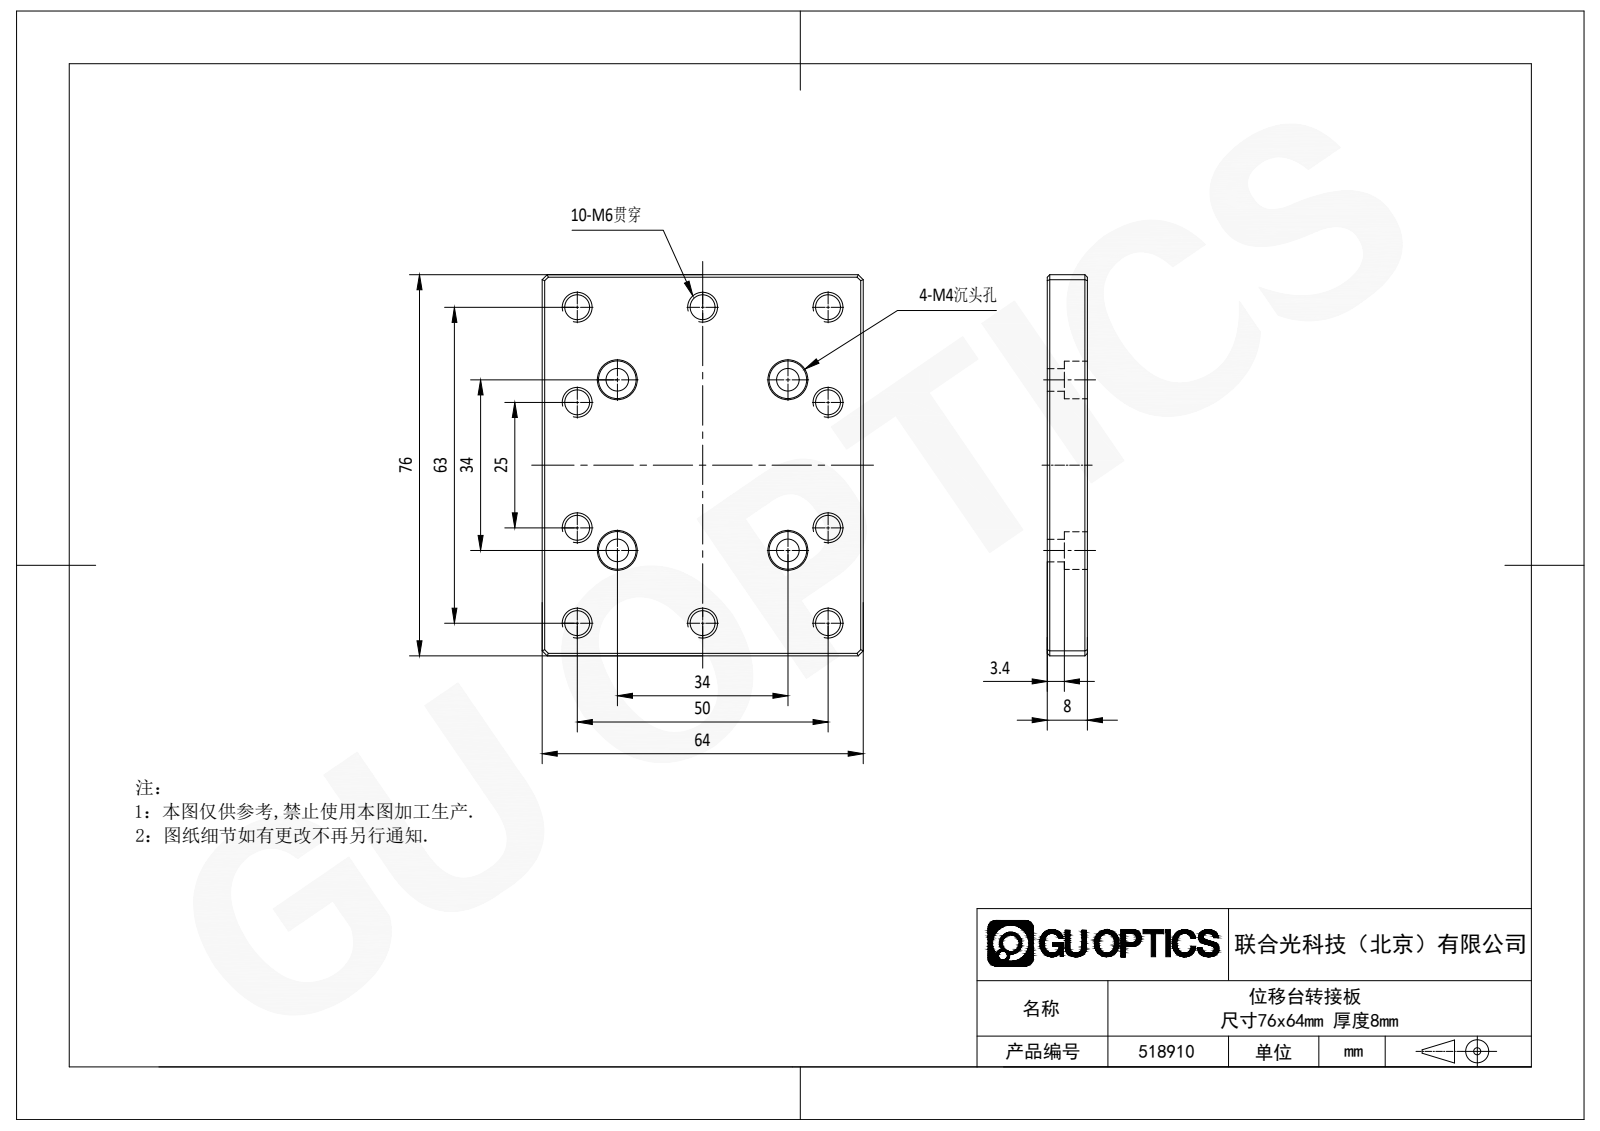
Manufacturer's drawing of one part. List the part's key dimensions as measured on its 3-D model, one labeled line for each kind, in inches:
STEP written by: SolidWorks 2020 (CONFIG_CONTROL_DESIGN)
Units: inches
Bodies: 1 solid, 62 faces (30 planar, 18 cylindrical, 14 other)
Overall size (bounding box): 2.992 × 2.52 × 0.315
Volume: 2.209 in³ · Surface area: 20.28 in²
Round holes (diameter × count): ⌀0.197 ×10, ⌀0.177 ×4, ⌀0.295 ×4
Main face-to-face distances: 0.315, 2.52, 2.992, 0.134, 0.181, 1.976, 2.31, 3.841, 2.911
Hole centre spacings: 0.984, 0.361, 0.652, 0.748, 0.88, 1.204, 1.236, 1.339
